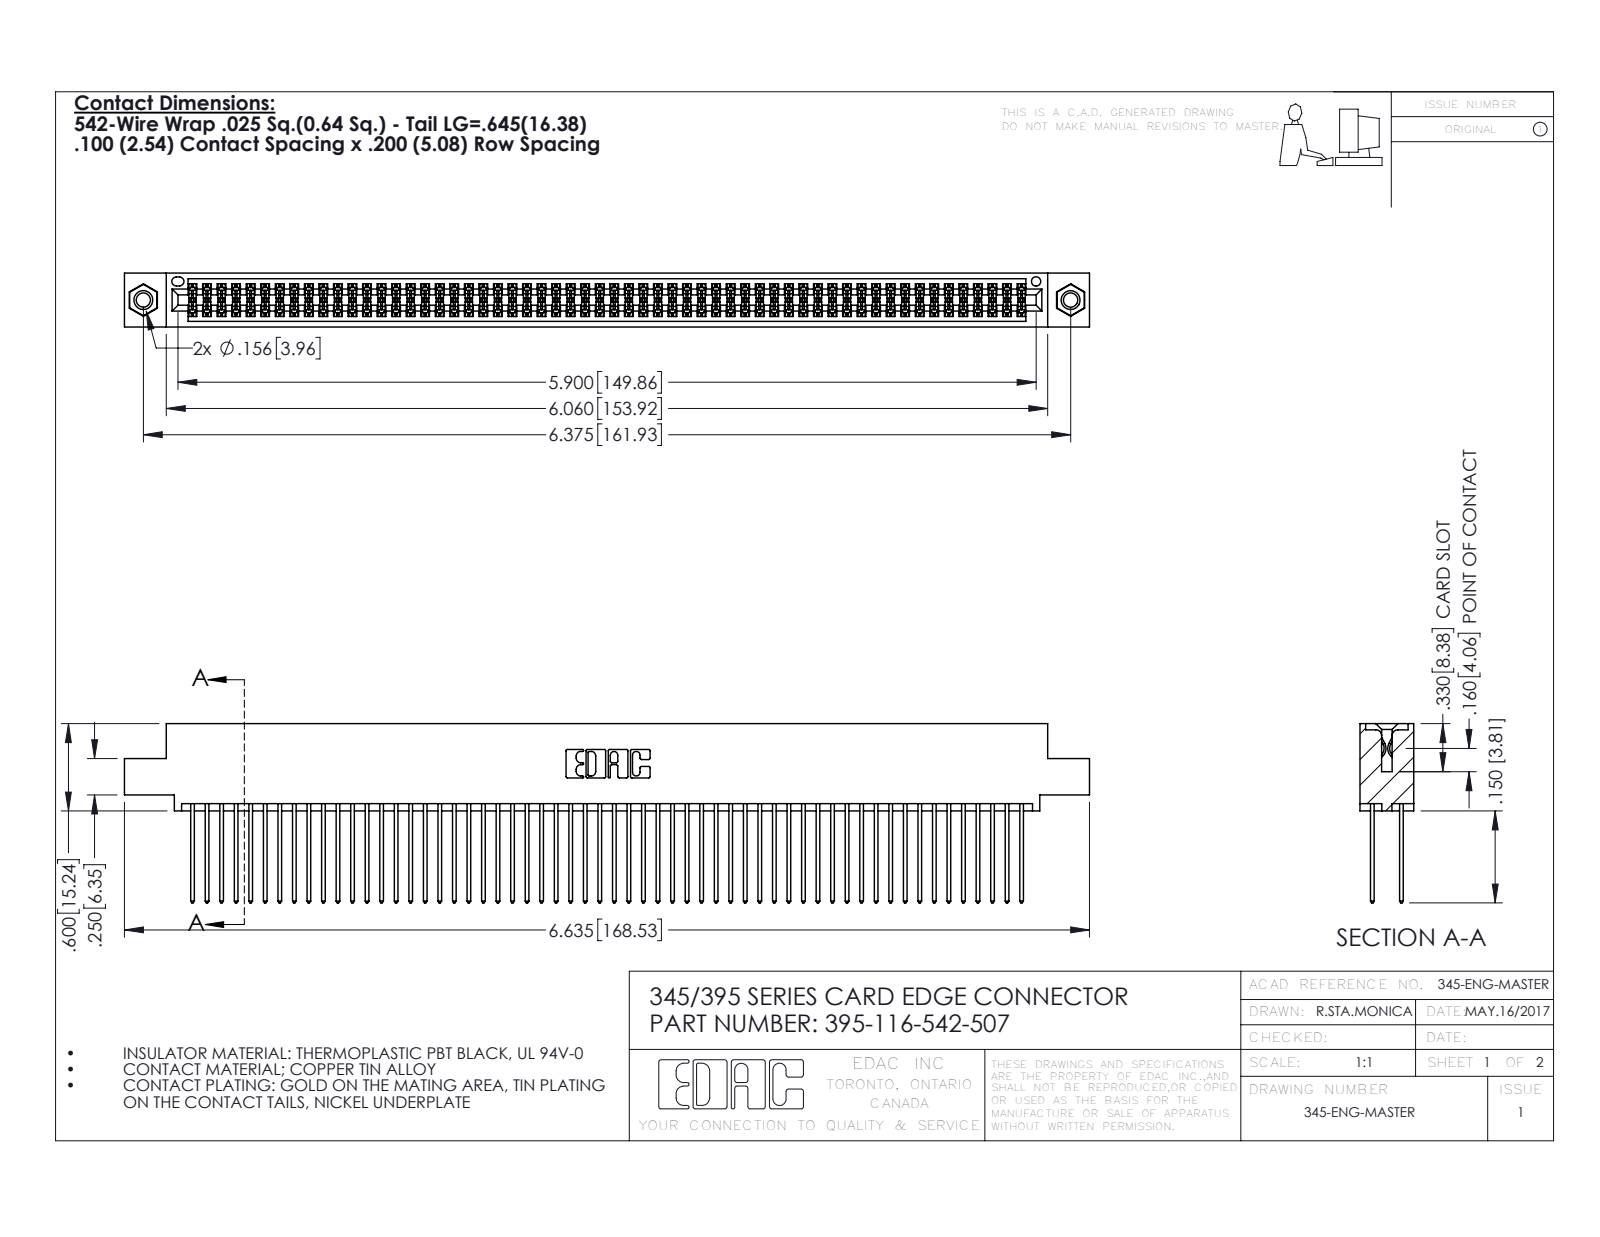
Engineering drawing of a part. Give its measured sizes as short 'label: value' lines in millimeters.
name: 345-250-001_345-250-005-103; 395-116-542-507; 345 Part_0.110 Offset - 0.156 Dia-TI; 345-292-001_345-293-142
written by: SolidWorks 2016 (CONFIG_CONTROL_DESIGN)
unit: mm
bodies: 119 solids, 5990 faces (3944 planar, 2030 cylindrical, 16 other)
size: 168.5 × 31.3 × 9.4
volume: 16 980 mm³; area: 28 050 mm²
holes: 2× ⌀2.5, 2× ⌀3.2, 2× ⌀4, 1× ⌀1.6
bosses: 2× ⌀3.9
rounds: 174× R0.2, 116× R0.3, 22× R0.3, 6× R0.2, 6× R0.8, 3× R0.7, 2× R0.4, 2× R0.5
face distances: 1.8, 7.6, 5.1, 2.5, 6.9, 0.6, 5.7, 9.4, 4.4, 3.8
hole spacings: 6.9, 155.9, 161.9
